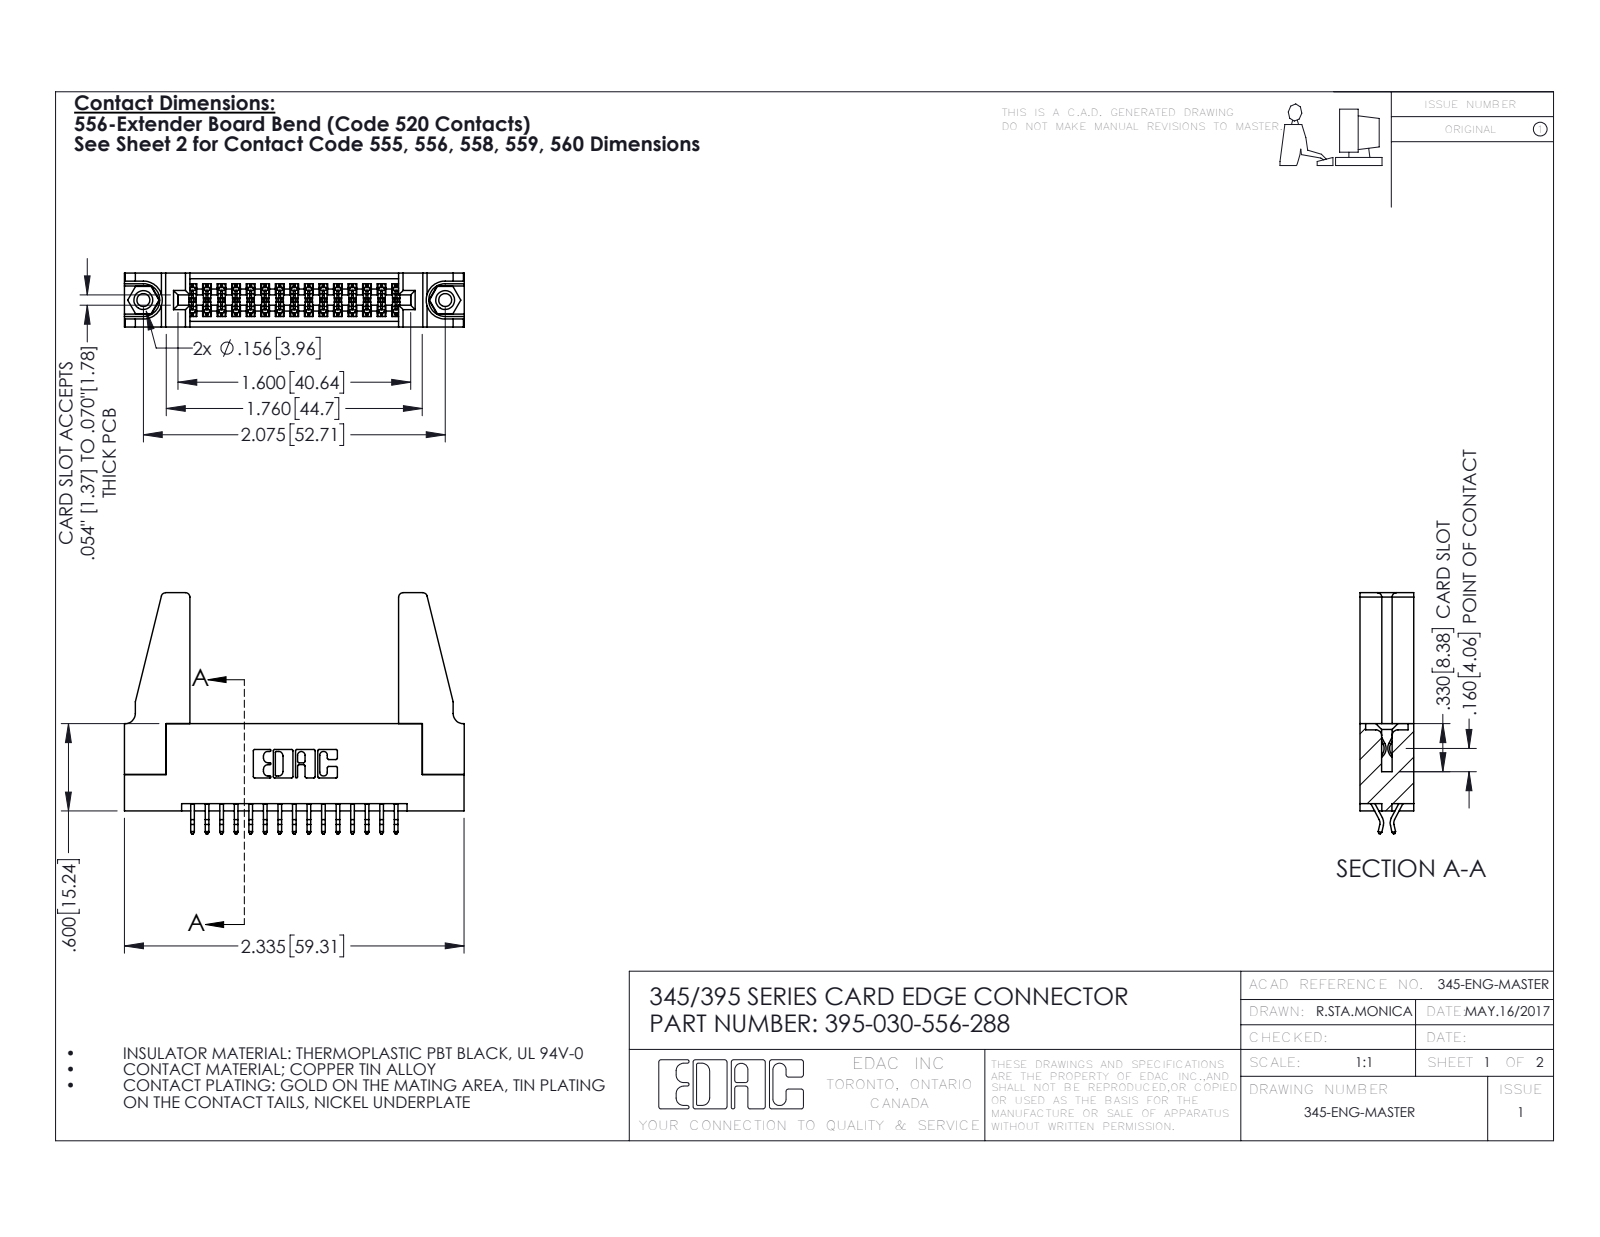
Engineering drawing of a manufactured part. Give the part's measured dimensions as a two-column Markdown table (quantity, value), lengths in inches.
| quantity | value |
| --- | --- |
| part name | 345-250-001_345-250-001-102; 395-030-556-288; 345-220-078_345-220-088; 345 Part_Flush Mounting Lugs - 0.156 Dia-TH (+1 more) |
| STEP written by | SolidWorks 2016 (CONFIG_CONTROL_DESIGN) |
| units | inches |
| bodies | 35 solids, 1930 faces (1262 planar, 652 cylindrical, 16 other) |
| overall size | 2.336 × 1.657 × 0.37 |
| volume | 0.535 in³ |
| surface area | 16.62 in² |
| round holes (diameter × count) | 0.089 × 2, 0.125 × 2, 0.156 × 2, 0.064 × 1 |
| round bosses / shafts (diameter × count) | 0.155 × 2 |
| partial cylindrical surfaces (radius × count) | 0.006 × 45, 0.01 × 22, 0.03 × 8, 0.007 × 6, 0.031 × 6, 0.026 × 3, 0.01 × 2, 0.014 × 2 |
| main face-to-face distances | 0.37, 0.072, 0.298, 0.2, 0.025, 0.098, 0.272, 0.225, 0.148, 0.15 |
| hole center spacings | 0.27, 1.842, 2.075 |
